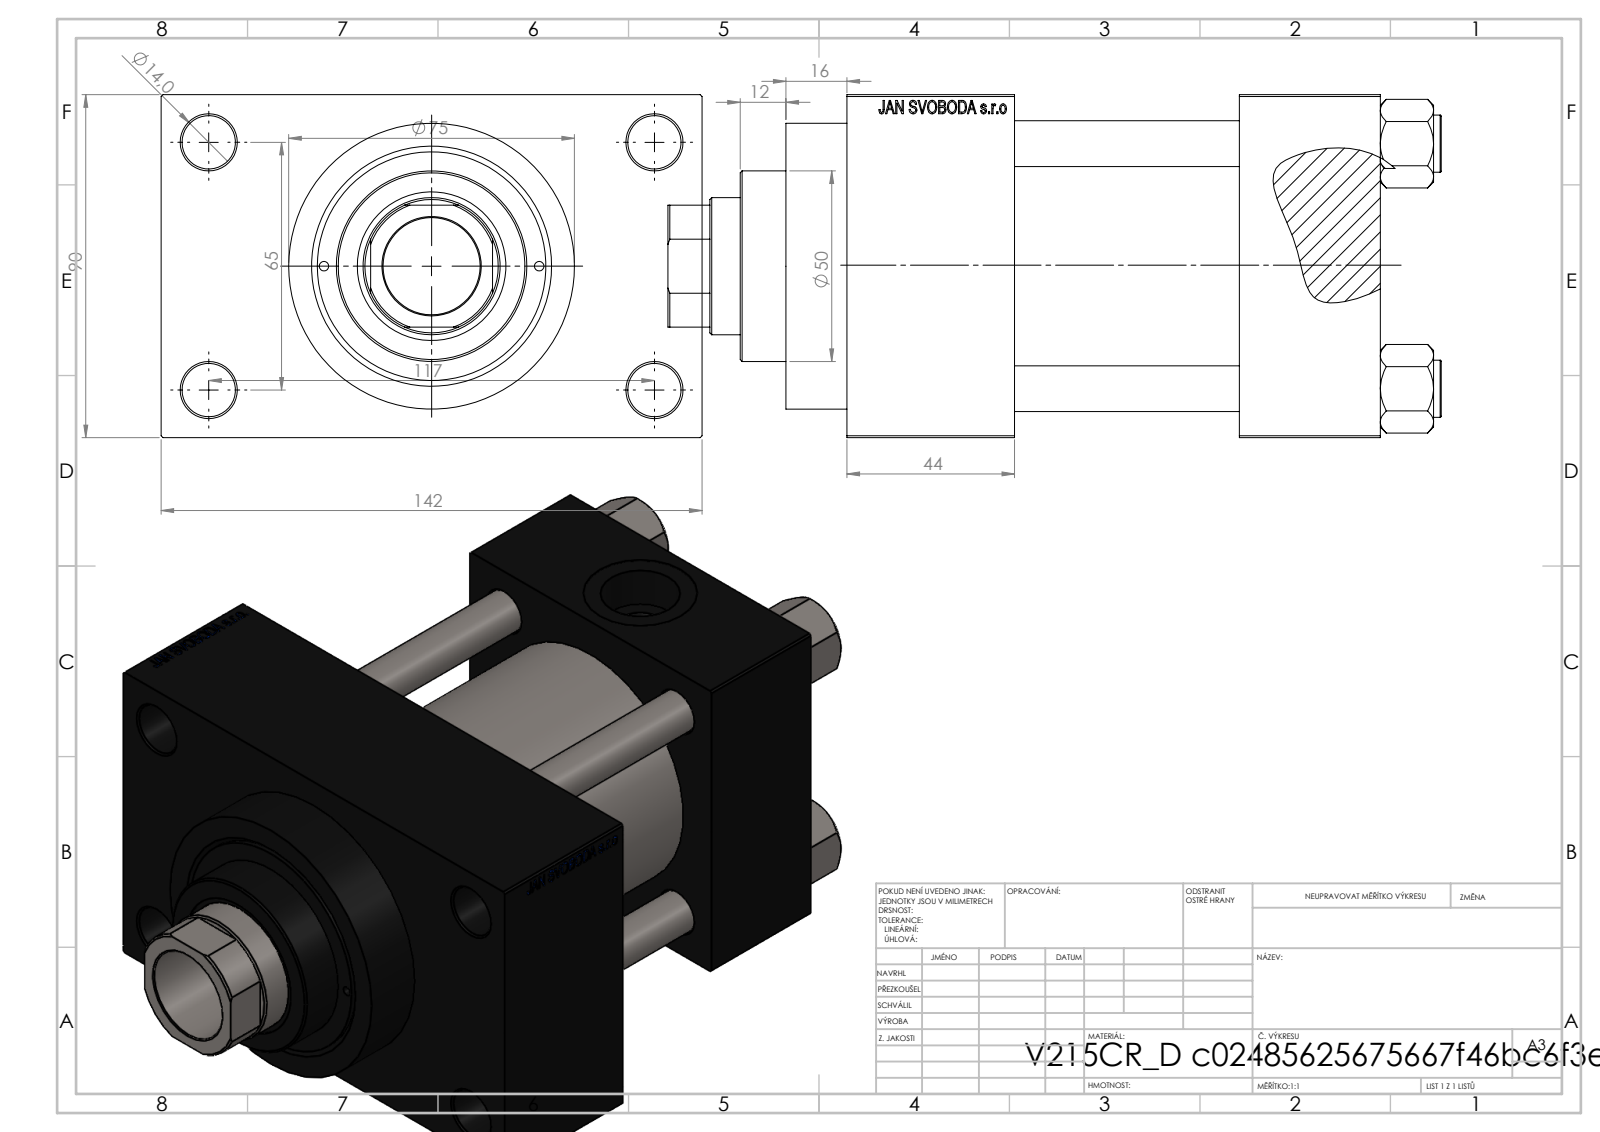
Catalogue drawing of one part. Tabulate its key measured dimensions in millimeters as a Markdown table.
| quantity | value |
| --- | --- |
| part name | V215CR_VCP_D; V215CR_D_TYCINKA; V215_VC_A; V215CR_D_Body (+1 more) |
| STEP written by | SolidWorks 2019 (CONFIG_CONTROL_DESIGN) |
| units | millimeters |
| bodies | 11 solids, 1112 faces (499 planar, 93 cylindrical, 520 other) |
| overall size | 203 × 142 × 90 |
| volume | 1 120 000 mm³ |
| surface area | 203 993 mm² |
| round holes (diameter × count) | 12 × 4, 14 × 4, 2.5 × 2, 7 × 2, 20.96 × 2, 30 × 2, 25.5 × 1, 36 × 1, 39 × 1, 50 × 1, 60 × 1, 63 × 1 |
| round bosses / shafts (diameter × count) | 15 × 4, 75 × 1, 69 × 1 |
| partial cylindrical surfaces (radius × count) | 17.5 × 1 |
| main face-to-face distances | 90, 59, 37, 96, 140, 103, 44, 26, 116, 142 |
| hole center spacings | 26.35, 32.39, 44.4, 45.47, 64.3, 66.92, 68.42, 69.81 |
